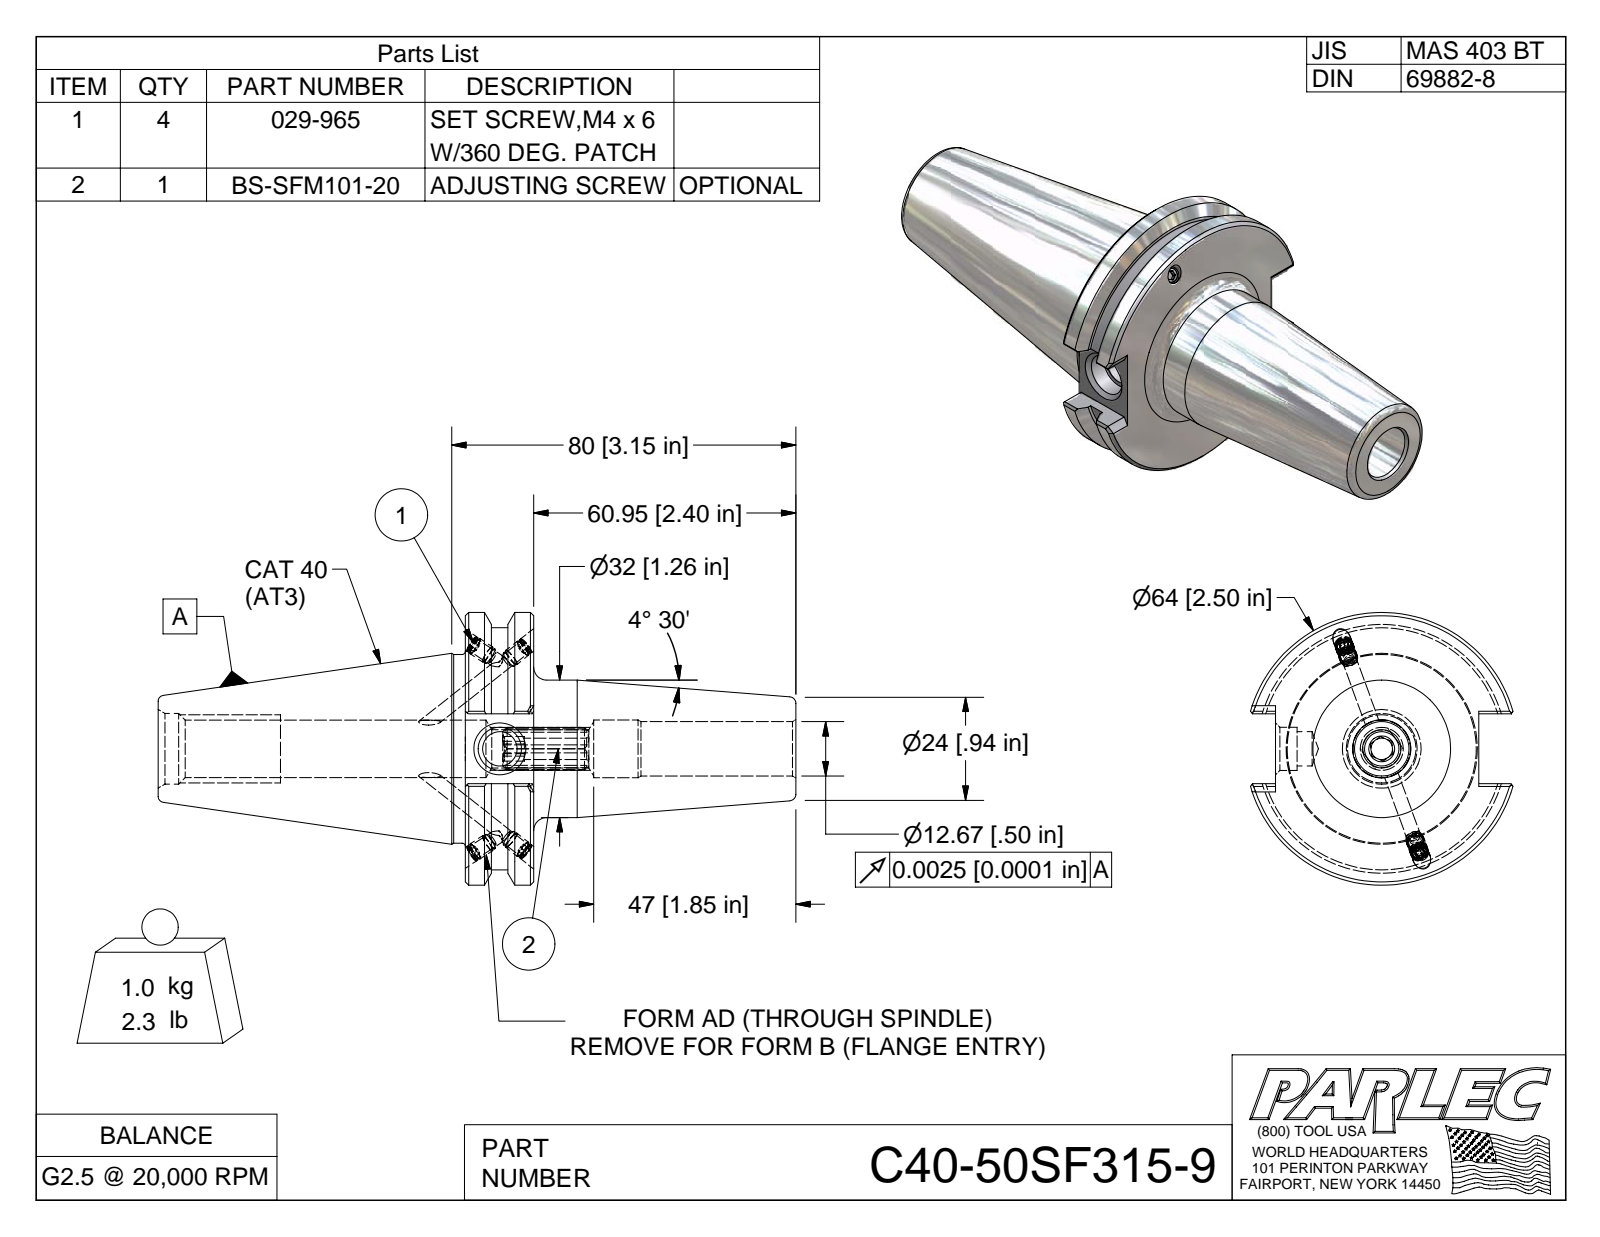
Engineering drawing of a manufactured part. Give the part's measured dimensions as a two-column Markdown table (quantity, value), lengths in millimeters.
| quantity | value |
| --- | --- |
| part name | C40-50SF315-9; C40BC-50SF315-9-1; 029-965; BS-SFM101-20 |
| STEP written by | Autodesk Inventor 2009 (AUTOMOTIVE_DESIGN) |
| units | millimeters |
| bodies | 6 solids, 172 faces (87 planar, 32 cylindrical, 53 other) |
| overall size | 148.3 × 63.5 × 61 |
| volume | 134 500 mm³ |
| surface area | 29 640 mm² |
| round holes (diameter × count) | 3.3 × 4, 4.1 × 4, 12.7 × 1, 13.4 × 1 |
| round bosses / shafts (diameter × count) | 4.2 × 4, 4 × 4, 63.5 × 1, 56.4 × 1, 43.9 × 1, 32 × 1 |
| partial cylindrical surfaces (radius × count) | 5 × 1 |
| main face-to-face distances | 15.9, 76.8, 61, 16.3, 47.2, 71.4, 87.3, 148.3, 8, 81.3 |
